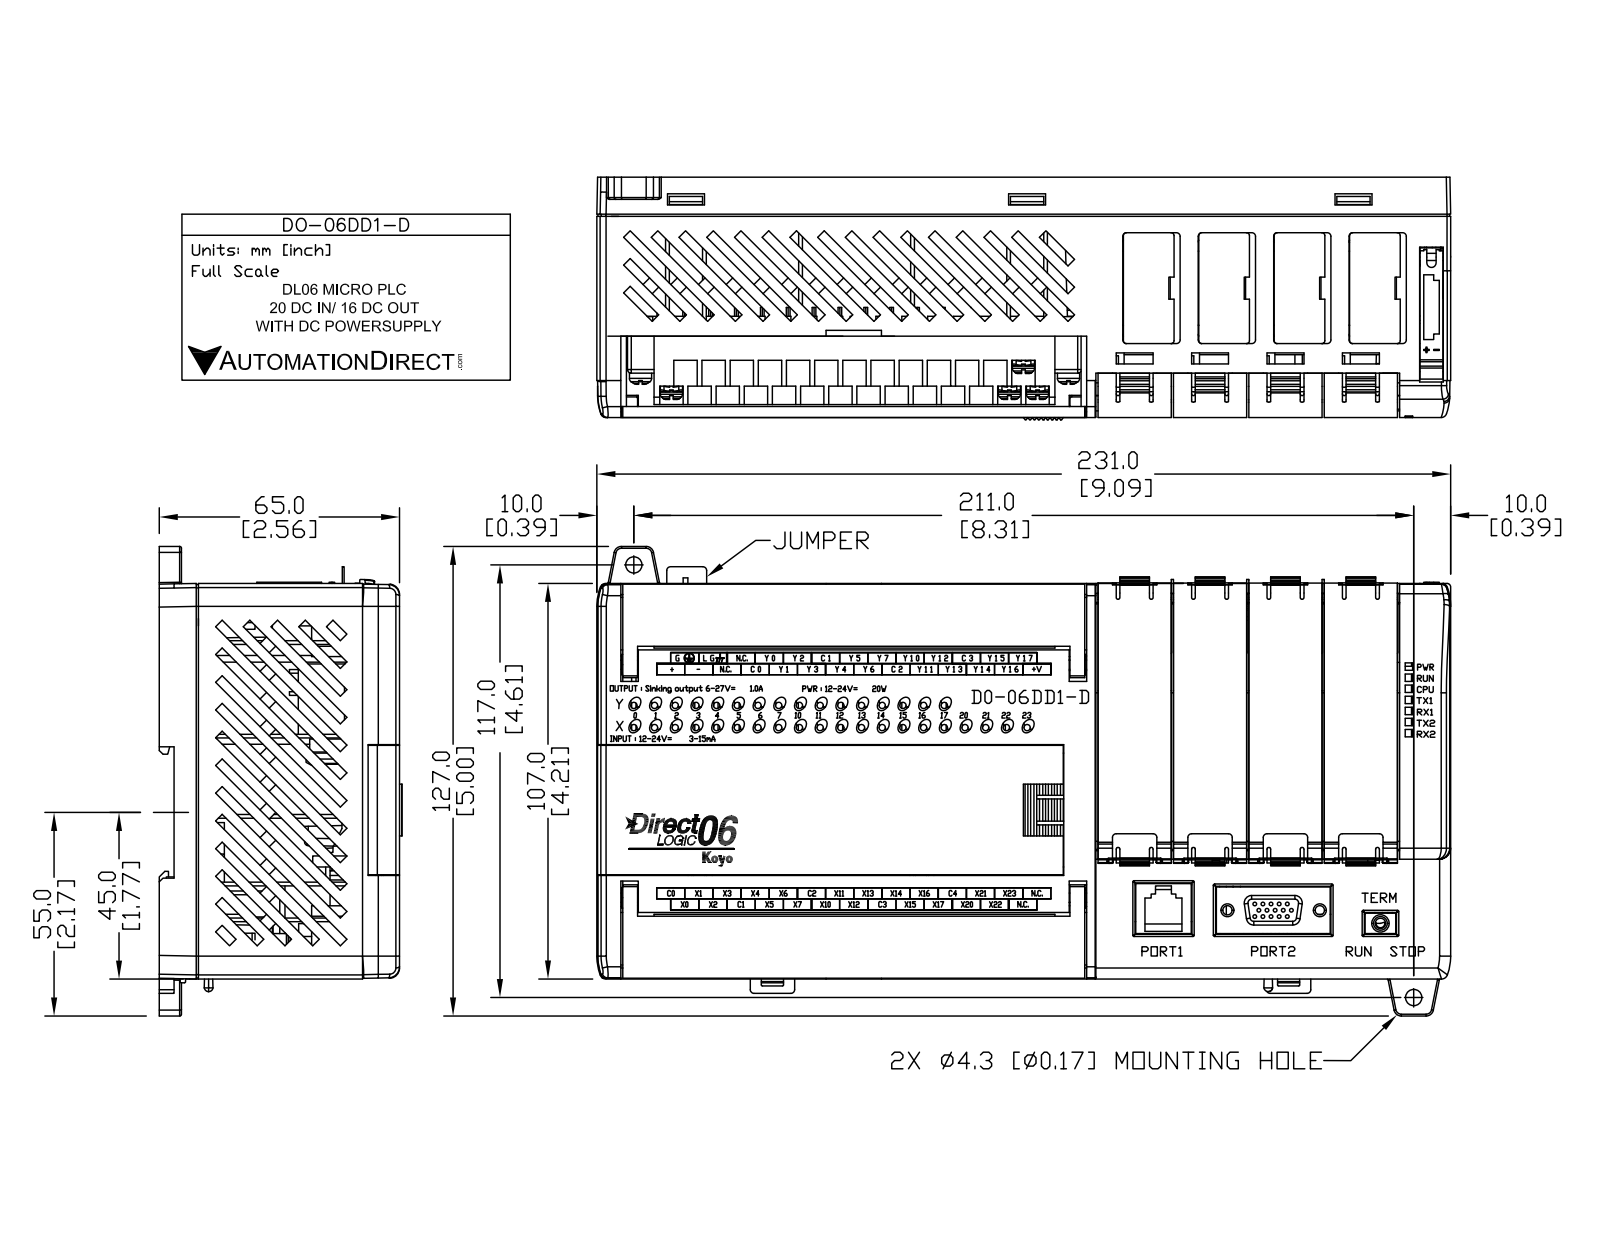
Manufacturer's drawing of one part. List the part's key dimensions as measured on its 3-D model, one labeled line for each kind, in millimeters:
Part name (STEP PRODUCT): D0-06DD1-D
STEP written by: SolidWorks 2009 (AUTOMOTIVE_DESIGN)
Units: millimetres
Bodies: 1 solid, 1455 faces (939 planar, 189 cylindrical, 327 other)
Overall size (bounding box): 230.9 × 127.1 × 65.2
Volume: 262 200 mm³ · Surface area: 199 400 mm²
Round holes (diameter × count): ⌀3 ×4, ⌀2 ×2, ⌀4.3 ×2
Round bosses / shafts (diameter × count): ⌀4.7 ×54, ⌀6.4 ×4, ⌀4.4 ×1, ⌀3.6 ×1
Partial cylindrical surfaces — rounded edges, fillets, slot ends (radius × count): R1.3 ×8, R1.7 ×5, R1.6 ×4, R2 ×4, R1 ×2, R1.6 ×2, R1.9 ×1, R62.8 ×1
Main face-to-face distances: 2.2, 2.2, 62.8, 4, 58.8, 65, 228.7, 60.6, 6.2, 56.6
Hole centre spacings: 82.8, 117.1, 143.5, 17.2, 23.8, 35.5, 42.7, 56
